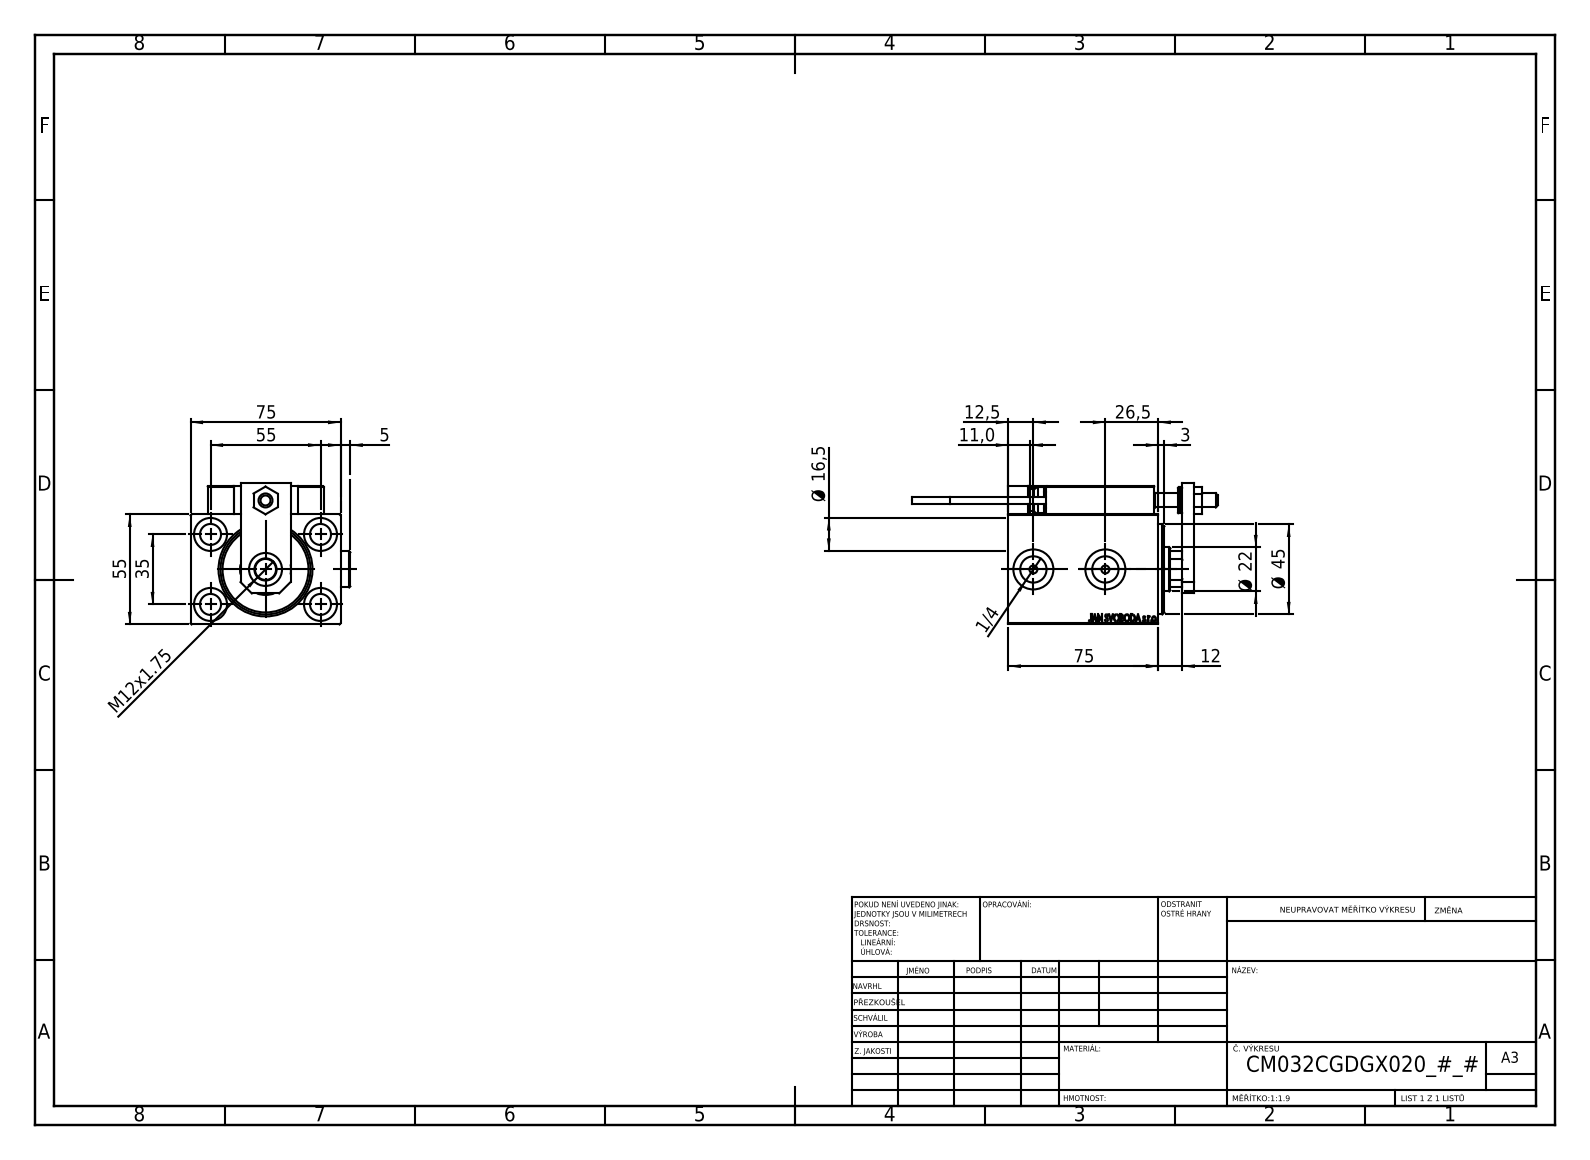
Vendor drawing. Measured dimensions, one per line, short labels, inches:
name: ZARAZKA; MAGNET; V450CM_VC_B; Zatka_OIL_PORT (+7 more)
written by: SolidWorks 2019 (CONFIG_CONTROL_DESIGN)
unit: in
bodies: 25 solids, 1336 faces (594 planar, 204 cylindrical, 538 other)
size: 6.012 × 3.146 × 2.776
volume: 19.02 in³; area: 135.5 in²
holes: 6× ⌀0.157, 5× ⌀0.315, 5× ⌀0.413, 5× ⌀0.65, 4× ⌀0.126, 2× ⌀0.197, 2× ⌀0.518, 2× ⌀0.787, 1× ⌀0.276, 1× ⌀0.866, 1× ⌀1.004, 1× ⌀1.26
bosses: 2× ⌀0.709, 2× ⌀0.197, 2× ⌀0.15, 1× ⌀0.512, 1× ⌀0.433
rounds: 30× R0.012, 2× R0.118, 1× R0.413
face distances: 2.165, 2.953, 0.551, 0.394, 0.472, 0.276, 0.197, 2.717, 0.984, 0.787
hole spacings: 1.283, 0.448, 0.787, 1.066, 1.165, 1.169, 1.273, 1.371
